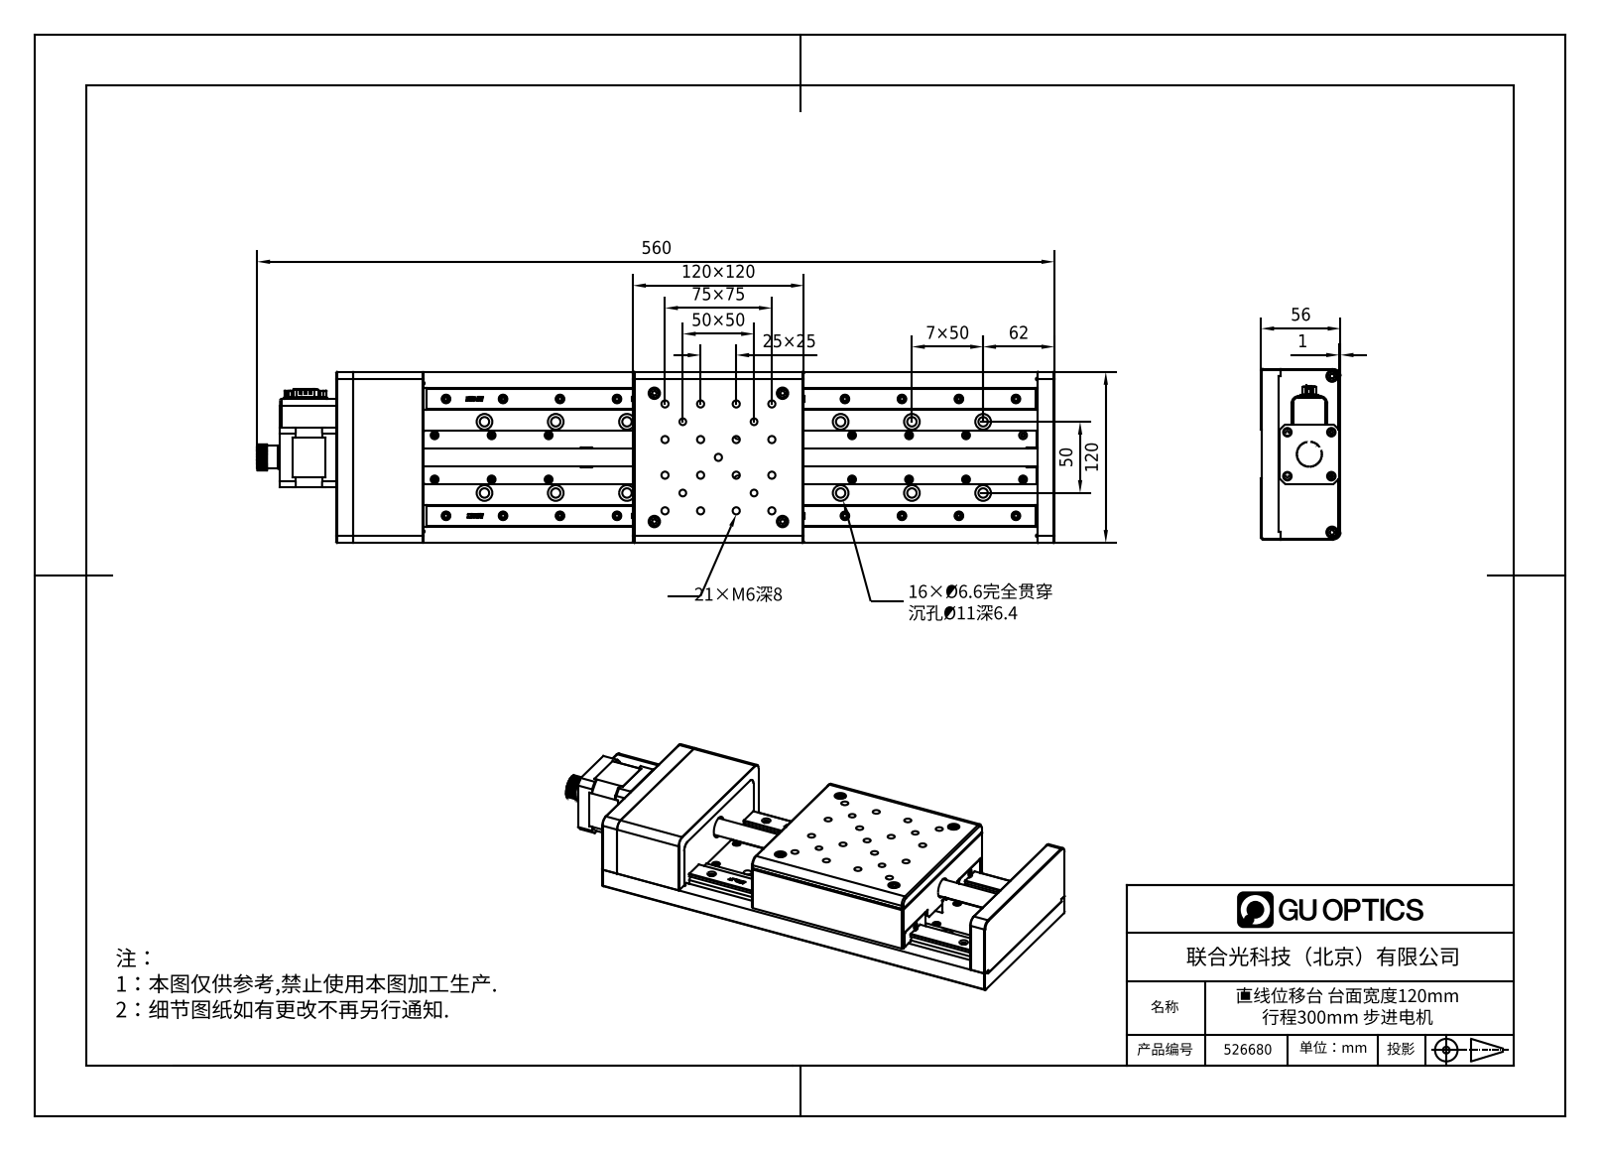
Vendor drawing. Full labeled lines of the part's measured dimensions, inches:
Part name (STEP PRODUCT): FMS120V-300
STEP written by: SolidWorks 2017 (CONFIG_CONTROL_DESIGN)
Units: inches
Bodies: 0 solids, 992 faces (489 planar, 315 cylindrical, 188 other)
Overall size (bounding box): 21.732 × 4.724 × 2.205
Round holes (diameter × count): ⌀0.197 ×17, ⌀0.236 ×16, ⌀0.26 ×16, ⌀0.315 ×14, ⌀0.433 ×12, ⌀0.079 ×5, ⌀0.185 ×4, ⌀0.098 ×2, ⌀0.177 ×2, ⌀0.551 ×1
Round bosses / shafts (diameter × count): ⌀0.173 ×14, ⌀0.039 ×9, ⌀0.217 ×4, ⌀0.276 ×2, ⌀0.165 ×2, ⌀0.472 ×1
Partial cylindrical surfaces — rounded edges, fillets, slot ends (radius × count): R0.02 ×20, R0.039 ×11, R0.012 ×8, R0.016 ×7, R0.197 ×6, R0.059 ×4, R0.807 ×1
Main face-to-face distances: 0.551, 0.539, 1.102, 1.654, 4.724, 0.543, 0.531, 2.205, 0.039, 2.193
Hole centre spacings: 1.969, 2.784, 3.937, 4.402, 5.906, 6.225, 7.874, 8.117
